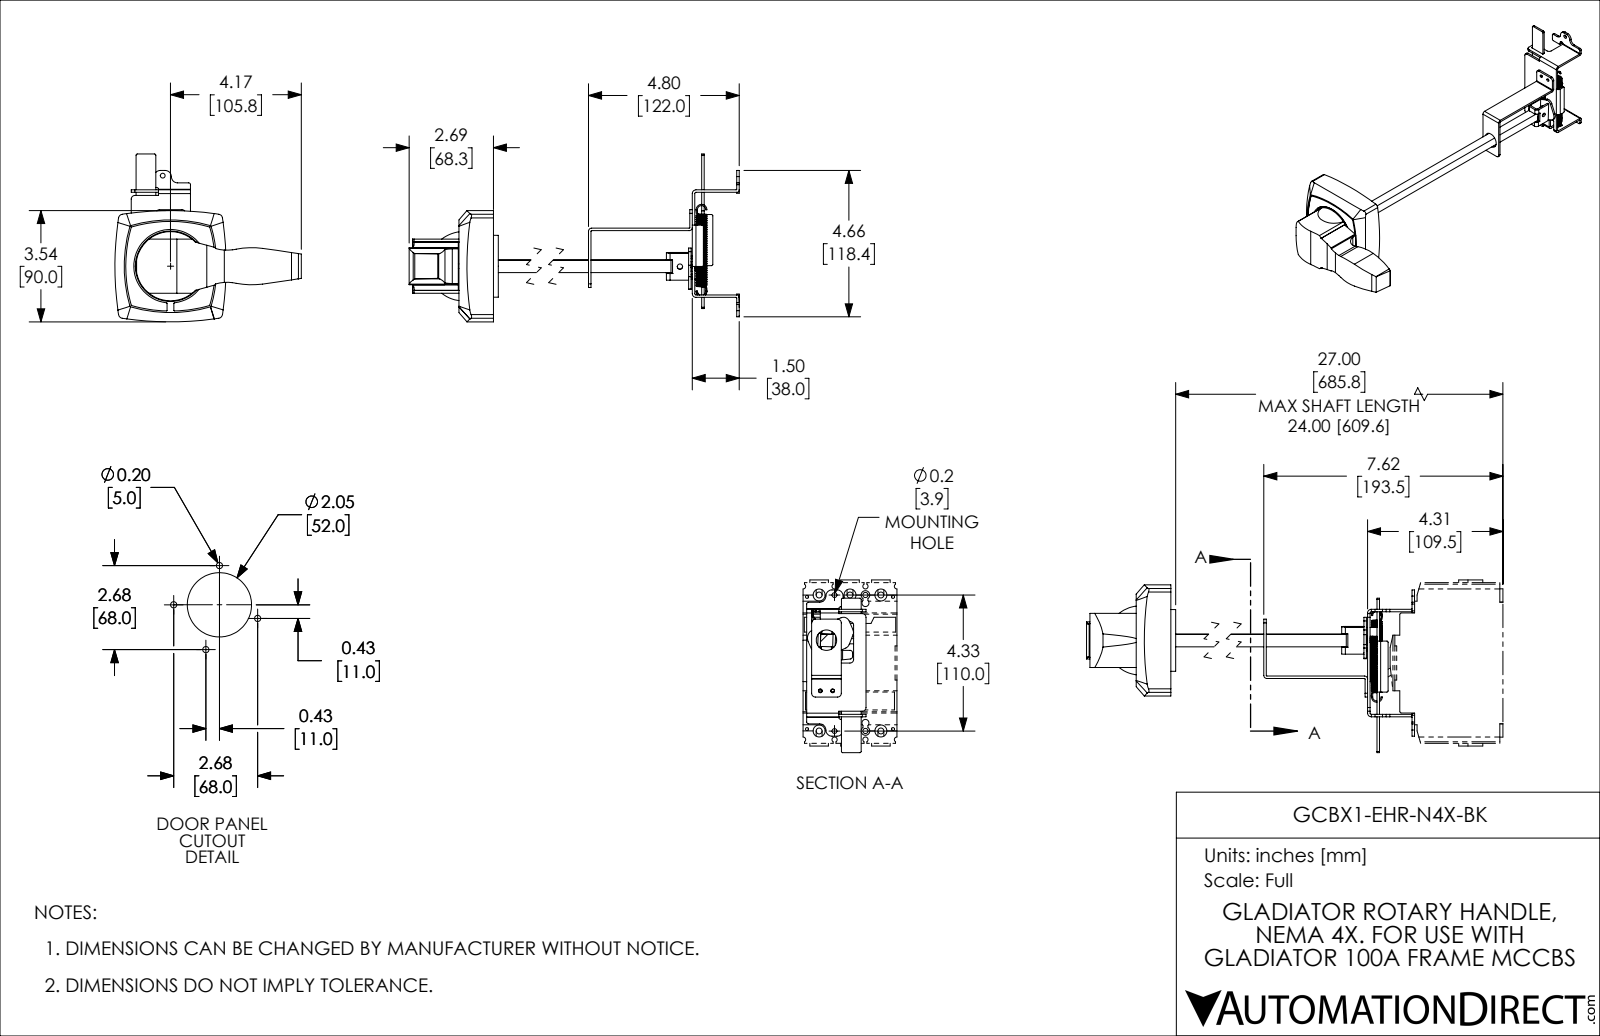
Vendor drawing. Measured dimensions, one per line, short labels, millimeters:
name: GCBX1-EHR-N4X-BK
written by: SolidWorks 2021 (CONFIG_CONTROL_DESIGN)
unit: mm
bodies: 5 solids, 572 faces (234 planar, 242 cylindrical, 96 other)
size: 404.87 × 150.84 × 135.79
volume: 386 702 mm³; area: 95 568 mm²
holes: 4× ⌀5, 3× ⌀3, 2× ⌀2.7, 2× ⌀3.1, 2× ⌀3.9, 1× ⌀2.5, 1× ⌀4.1, 1× ⌀4.3, 1× ⌀8.3, 1× ⌀16.5, 1× ⌀50, 1× ⌀57
bosses: 3× ⌀2.5, 1× ⌀59.5, 1× ⌀50, 1× ⌀9, 1× ⌀8, 1× ⌀7, 1× ⌀6, 1× ⌀4
rounds: 29× R3, 23× R1, 21× R0.5, 12× R0.3, 12× R1.5, 10× R0.2, 8× R5, 6× R2
face distances: 2, 7.6, 302.19, 330.69, 10, 10.01, 325.09, 4, 300.19, 332.69
hole spacings: 8.66, 14.86, 34, 35.74, 41.3, 68.88, 5.41, 8.33
